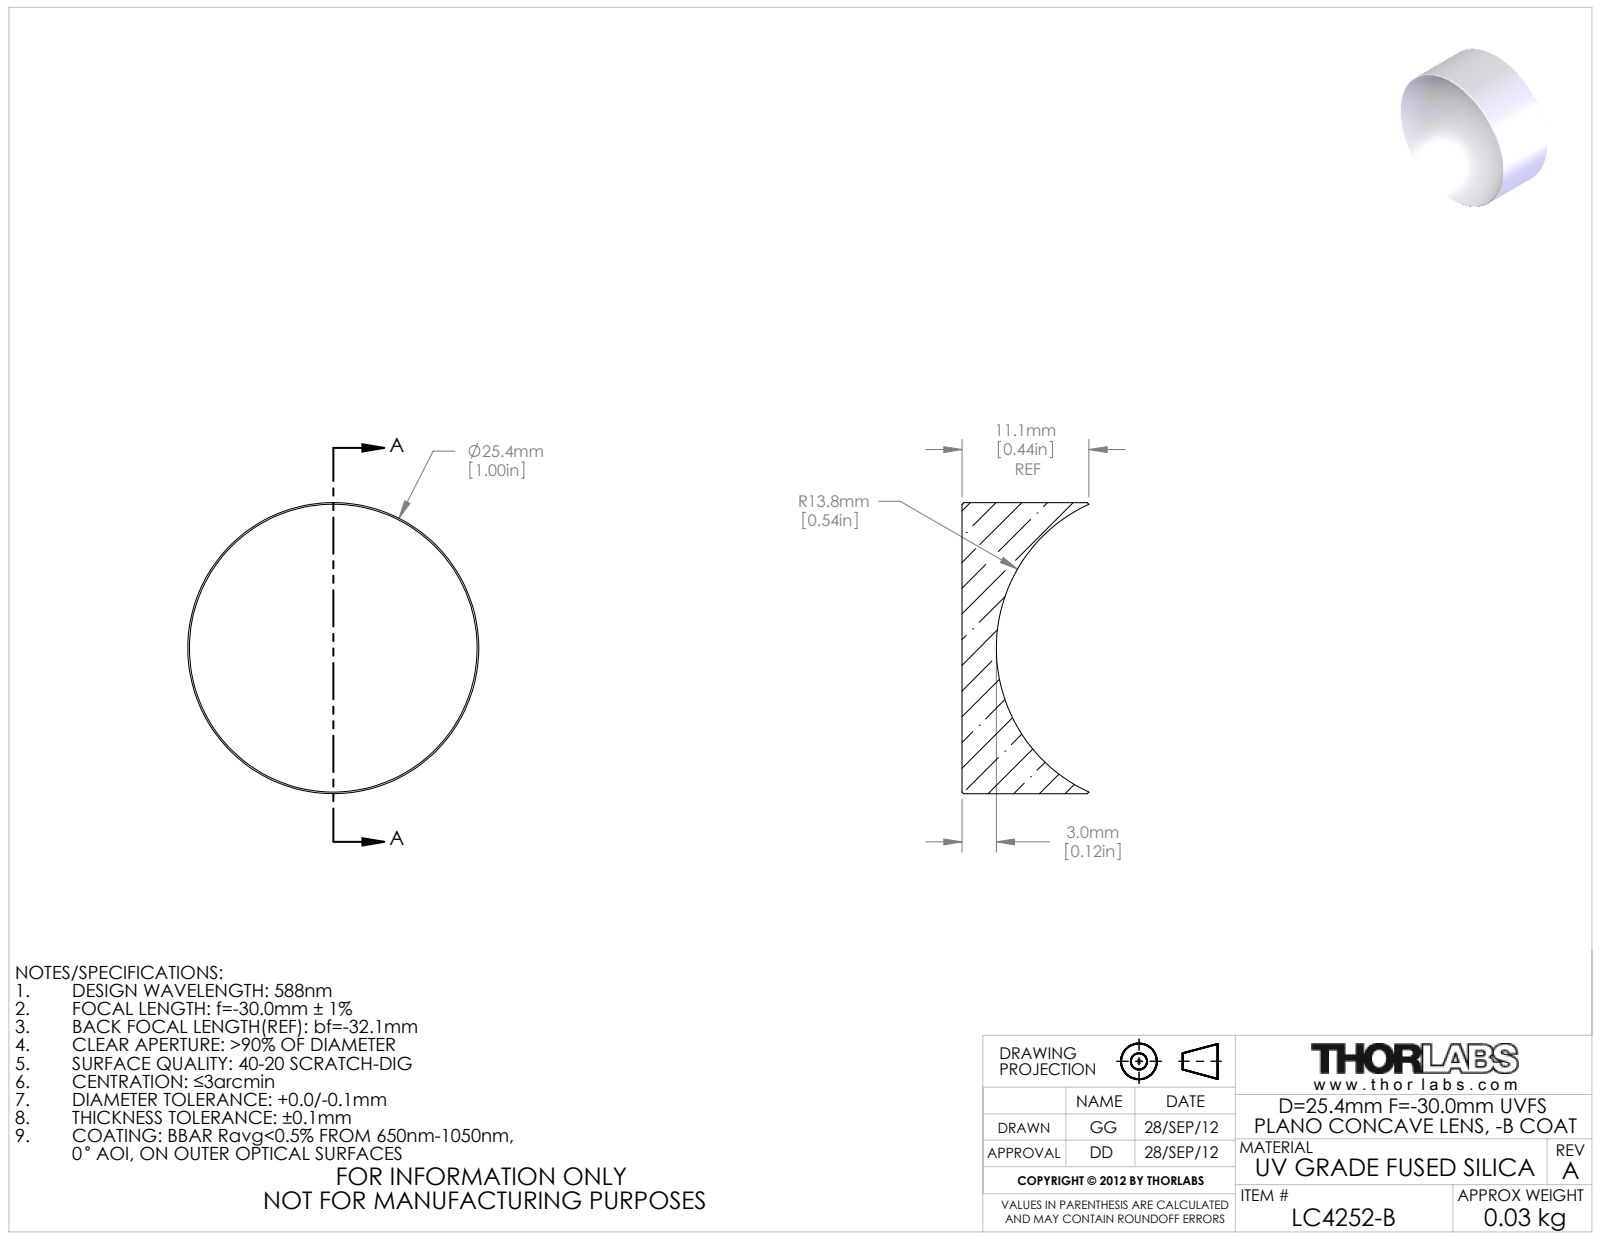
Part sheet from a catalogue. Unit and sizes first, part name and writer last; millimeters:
Units: millimetres
Overall size (bounding box): 25.4 × 25.4 × 11.08
Round bosses / shafts (diameter × count): ⌀25.4 ×1
Volume: 3 335 mm³ · Surface area: 2 089 mm²
Bodies: 1 solid, 9 faces (1 planar, 2 cylindrical, 6 other)
Part name (STEP PRODUCT): 25024-E0W
STEP written by: SolidWorks 2011 (CONFIG_CONTROL_DESIGN)
